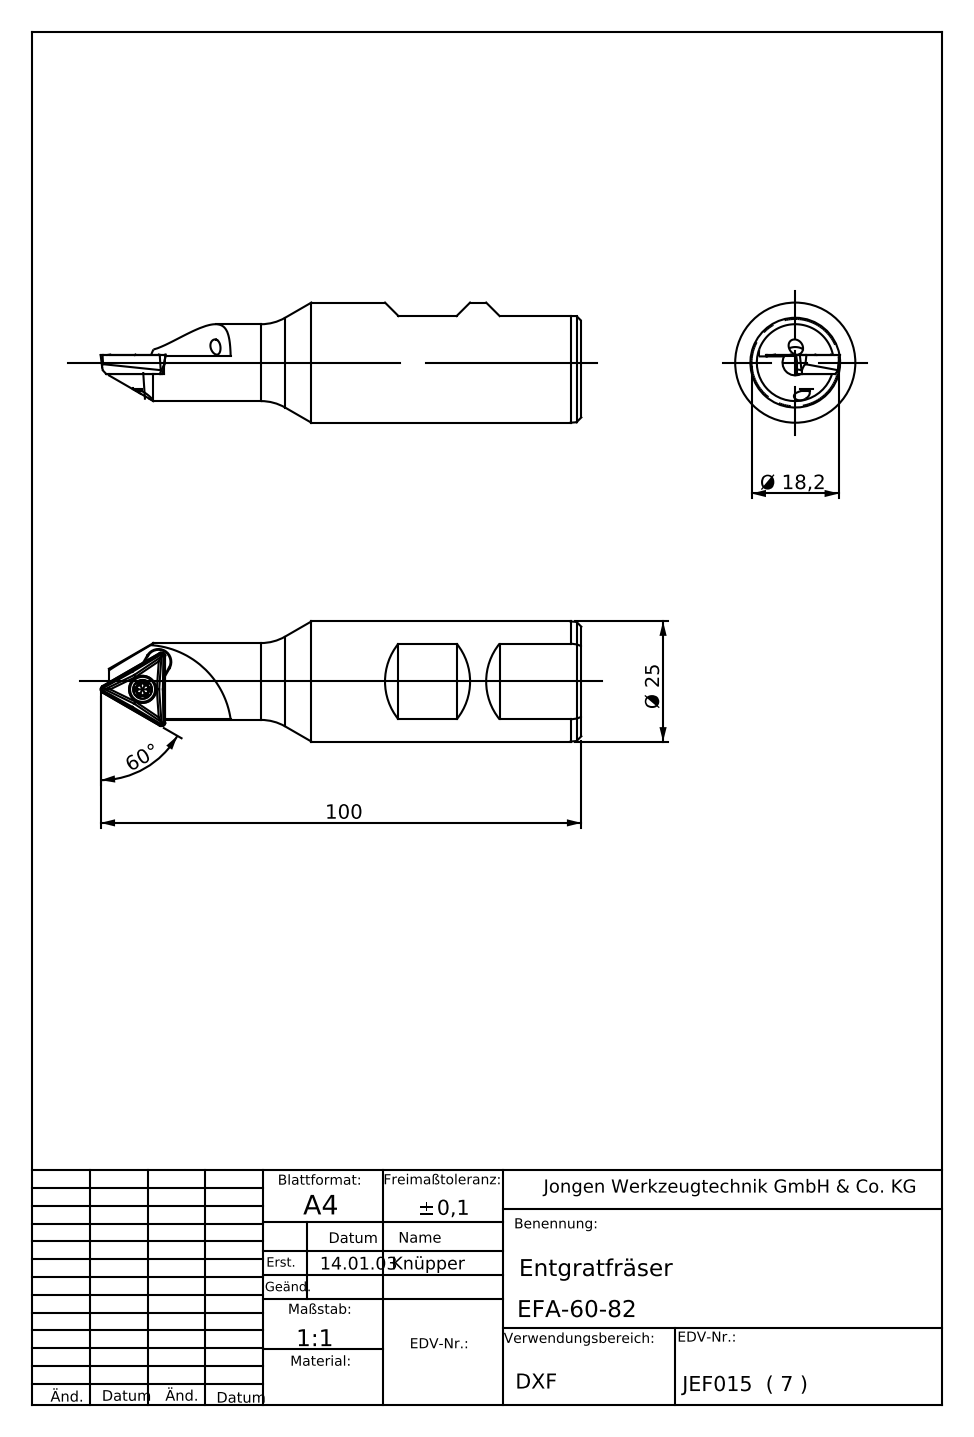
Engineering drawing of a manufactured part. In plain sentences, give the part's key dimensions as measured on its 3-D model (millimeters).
The part is named "EFA-60-82". Its 3-D file was written by "SolidWorks 2013 (AUTOMOTIVE_DESIGN)". It is 1 solid with 35 faces: 17 planar, 6 cylindrical and 12 other. Overall it measures 100 by 25 by 25 millimeters. Its volume is 32 121 cubic millimeters and its surface area 8 873 square millimeters. Round holes: 1 of diameter 3, 1 of diameter 6.5. Round bosses or shafts: 1 of diameter 25, 1 of diameter 16. Partial cylindrical surfaces (rounded edges, fillets, slot ends): 1 of radius 2.5, 1 of radius 18. The main face-to-face distances are 8.8, 86.58, 14.89, 11.31, 26.2, 3.67, 12.47, 98.3, 11.72, 86.75.
